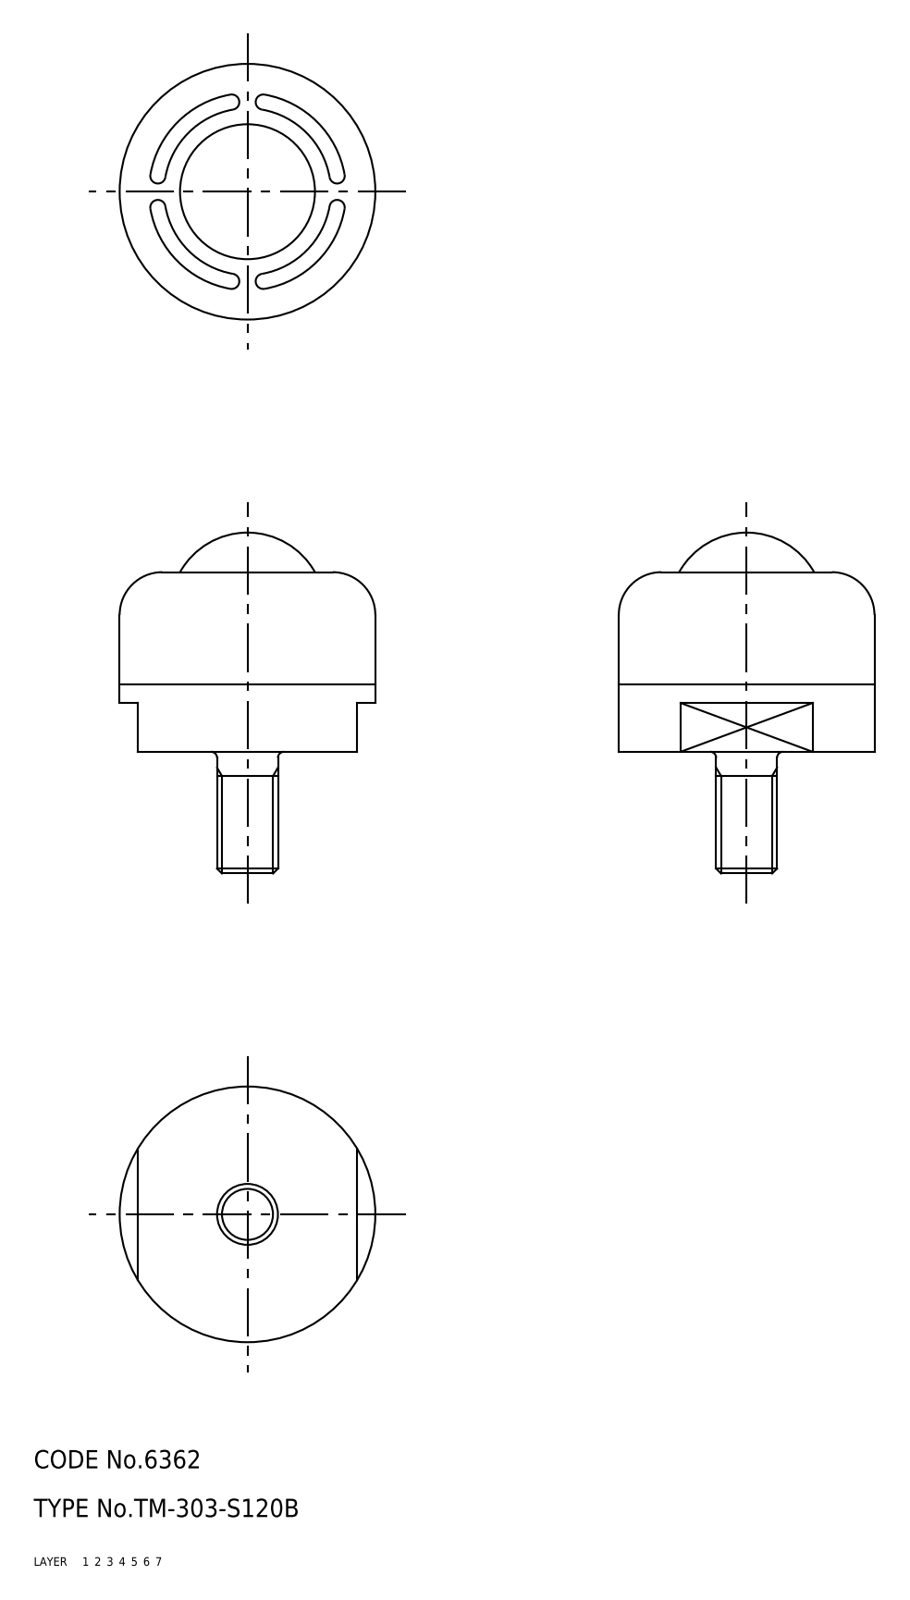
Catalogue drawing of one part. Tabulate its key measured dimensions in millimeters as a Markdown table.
| quantity | value |
| --- | --- |
| part name | 67112952; 67112965; 67112978 |
| STEP written by | CADfix (AUTOMOTIVE_DESIGN) |
| units | millimeters |
| bodies | 3 solids, 47 faces (0 planar, 0 cylindrical, 47 other) |
| overall size | 56 × 42 × 42 |
| volume | 26 597 mm³ |
| surface area | 12 484 mm² |
